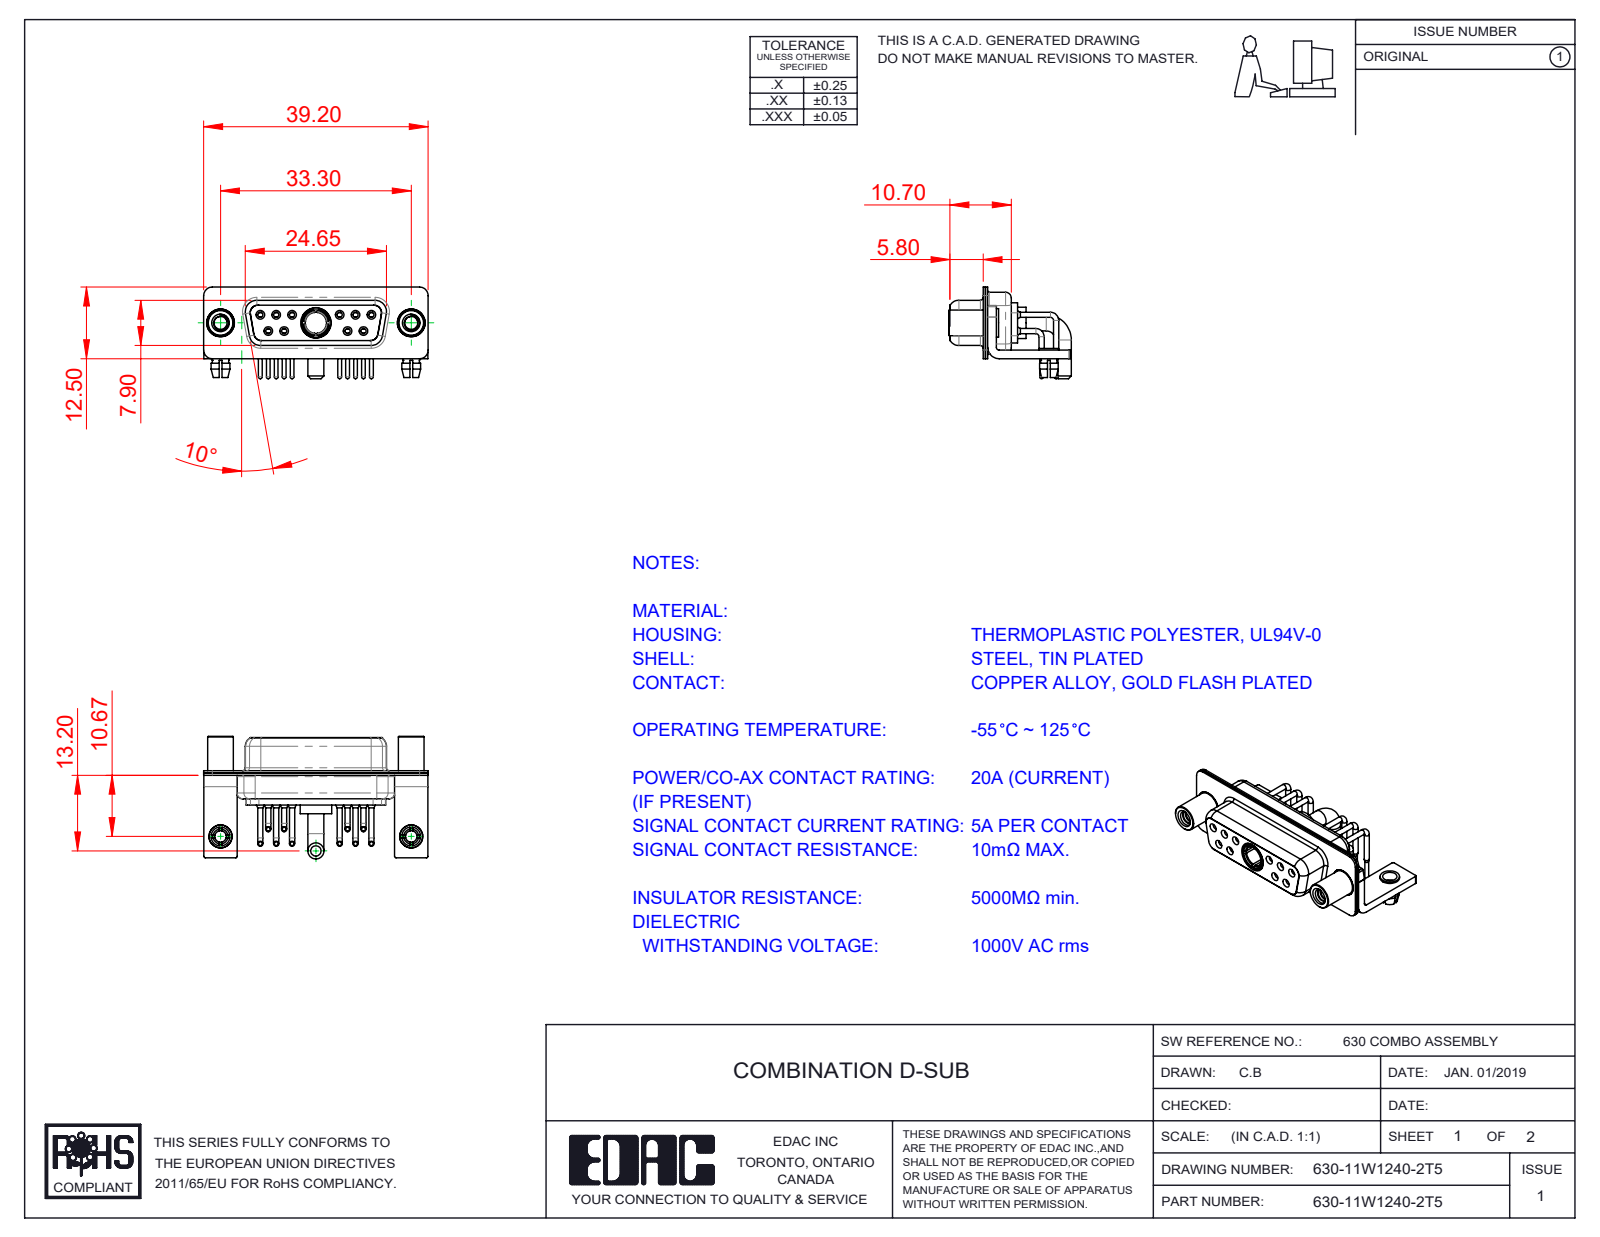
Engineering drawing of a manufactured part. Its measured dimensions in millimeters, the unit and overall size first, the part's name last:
Units: millimetres
Overall size (bounding box): 39.2 × 21.4 × 16
Round holes (diameter × count): ⌀2 ×12, ⌀0.9 ×10, ⌀1.1 ×10, ⌀1.5 ×10, ⌀1.7 ×6, ⌀1.6 ×4, ⌀4.85 ×3, ⌀2.26 ×2, ⌀2.5 ×2, ⌀3.2 ×2, ⌀4 ×2, ⌀4.05 ×2
Round bosses / shafts (diameter × count): ⌀0.9 ×10, ⌀0.65 ×10, ⌀1.6 ×6, ⌀5 ×2, ⌀4.95 ×2, ⌀4.8 ×2, ⌀4.5 ×2, ⌀4 ×2
Partial cylindrical surfaces — rounded edges, fillets, slot ends (radius × count): R0.25 ×16, R1.5 ×16, R2 ×13, R1.35 ×12, R1.6 ×8, R0.5 ×5, R0.6 ×4, R0.65 ×4
Main face-to-face distances: 0.4, 0.8, 0.45, 1.4, 8.45, 1.5, 1.8, 8.9, 6.2, 2.3
Hole centre spacings: 3.16, 2.77, 13.85, 11.08, 16.62, 5.03, 5.04, 5.54
Volume: 3 079 mm³ · Surface area: 7 397 mm²
Bodies: 21 solids, 1067 faces (316 planar, 484 cylindrical, 267 other)
Part name (STEP PRODUCT): 630Combo Shell Front_15 Contacts; 630Combo Housing_11W1; 630-11W1240-2T5; 630Combo Shell Rear_15 Contacts (+6 more)
STEP written by: SolidWorks 2020 (CONFIG_CONTROL_DESIGN)
